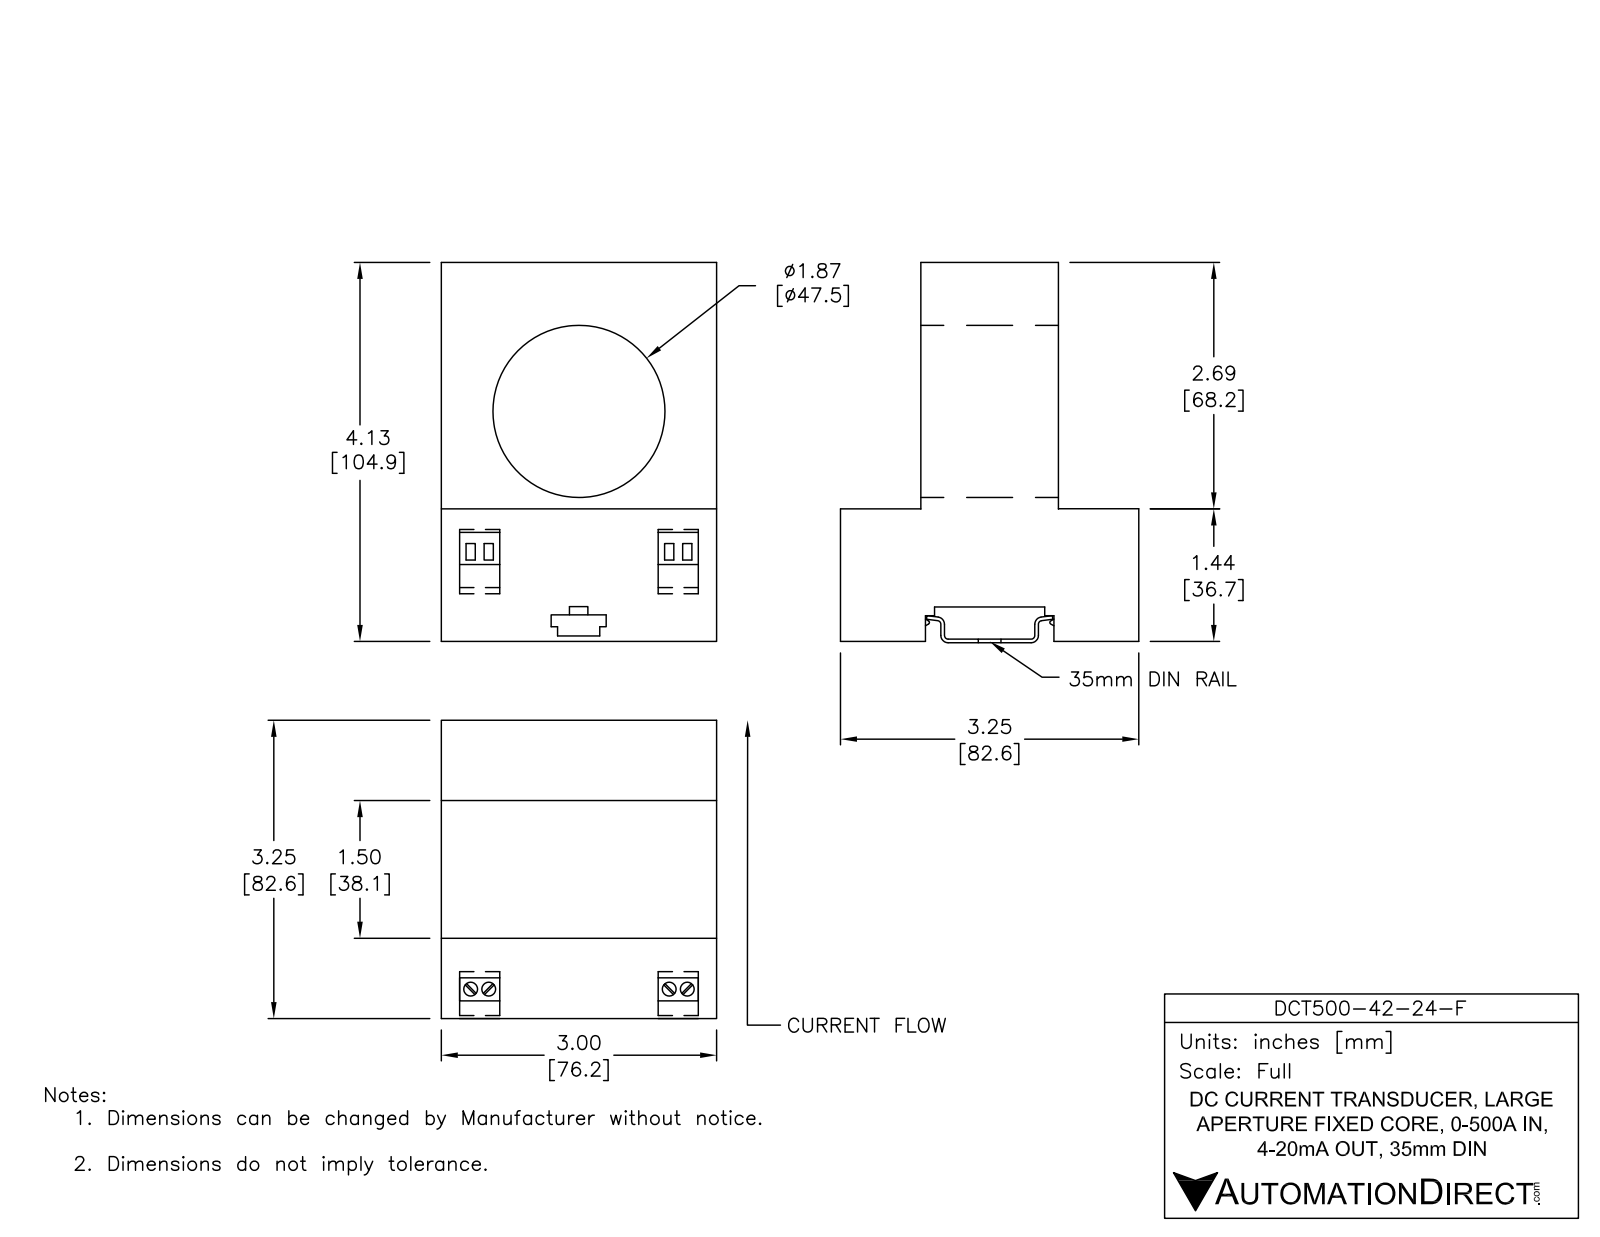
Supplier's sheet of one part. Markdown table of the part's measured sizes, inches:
| quantity | value |
| --- | --- |
| part name | DCT500-42-24-F |
| STEP written by | SolidWorks 2017 (AUTOMOTIVE_DESIGN) |
| units | inches |
| bodies | 13 solids, 360 faces (310 planar, 50 cylindrical, 0 other) |
| overall size | 4.2 × 3.524 × 3 |
| volume | 14.05 in³ |
| surface area | 110.2 in² |
| round holes (diameter × count) | 0.206 × 4, 0.1 × 2, 1.82 × 1 |
| round bosses / shafts (diameter × count) | 0.186 × 4 |
| partial cylindrical surfaces (radius × count) | 0.099 × 4, 0.128 × 4, 0.177 × 4 |
| main face-to-face distances | 0.075, 0.075, 3, 1.206, 1.131, 1.5, 1.25, 1.175, 0.044, 2.37 |
| hole center spacings | 0.394, 1.736, 2.574, 2.704, 0.676, 0.676, 1.068, 1.068 |
